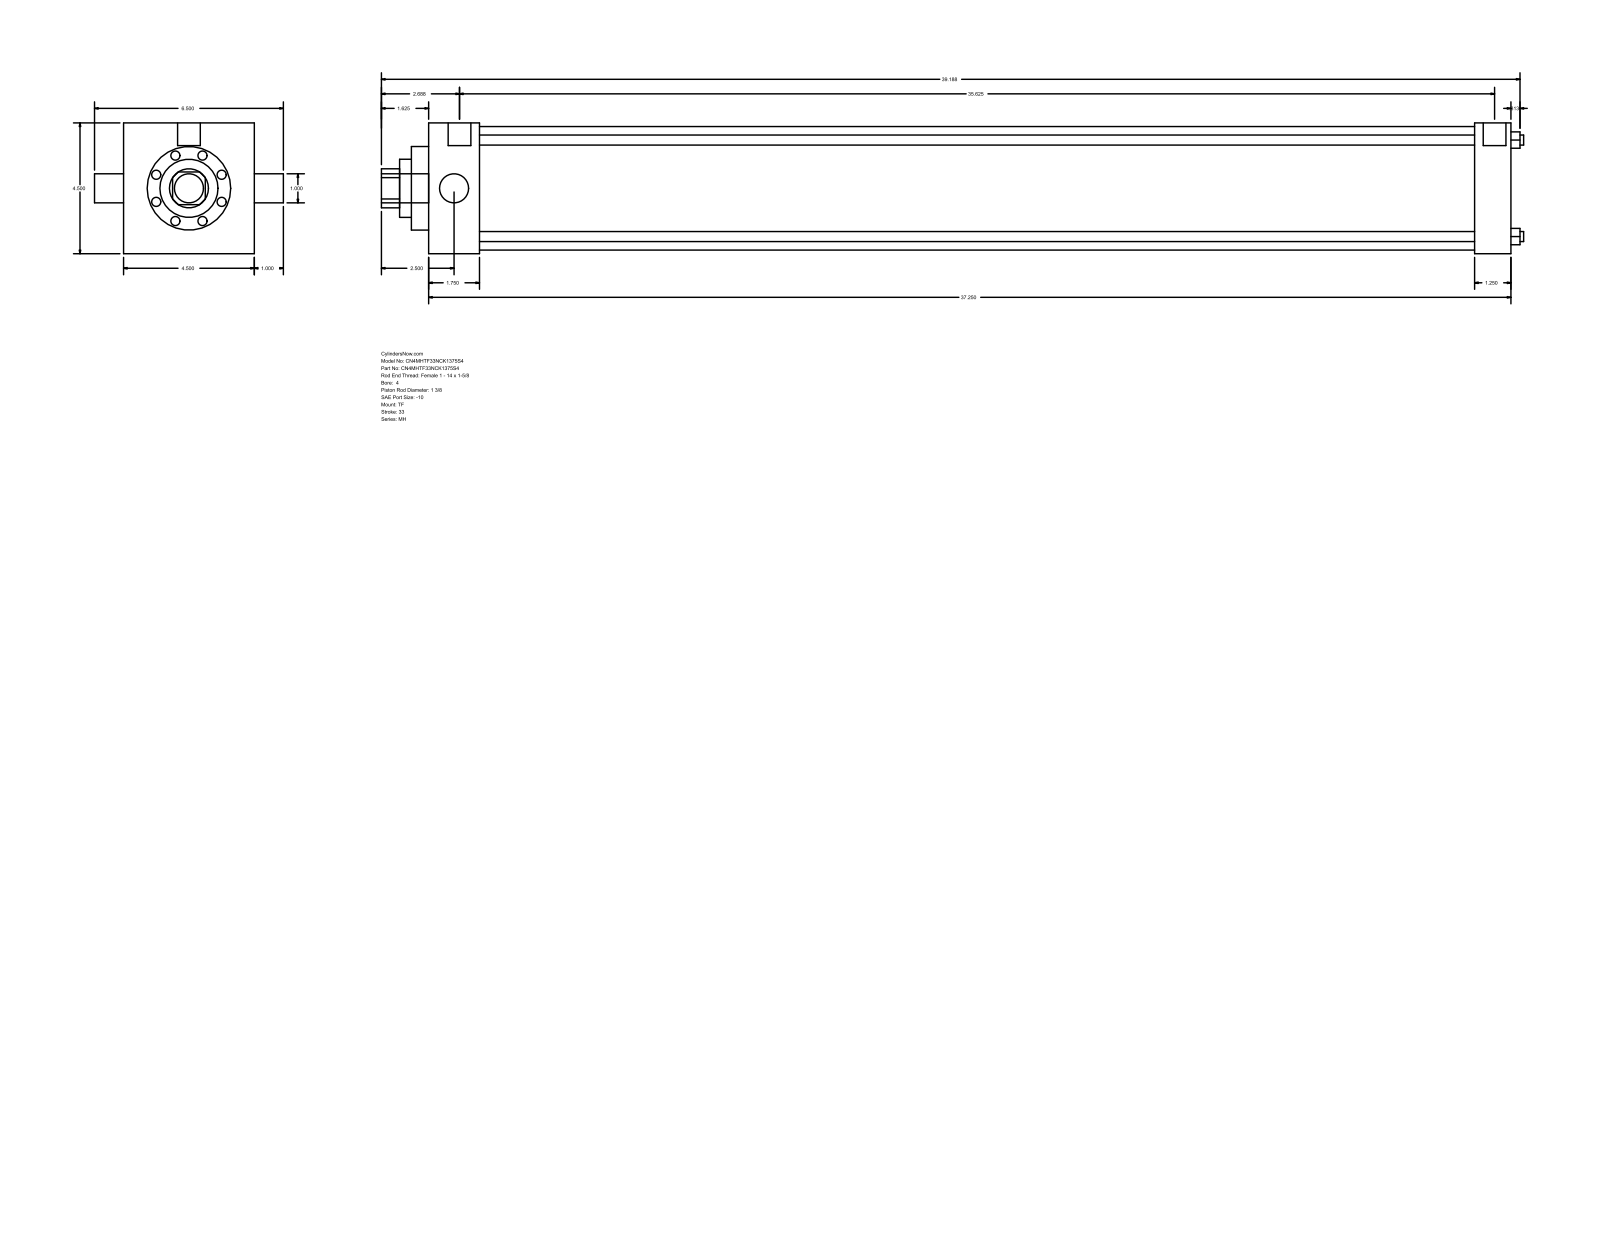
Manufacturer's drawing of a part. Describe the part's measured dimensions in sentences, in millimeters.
The part is named "MH_TF__0400_1.375". Its 3-D file was written by "GSSL Pune (CONFIG_CONTROL_DESIGN)". It is 0 solids with 86 faces: 61 planar, 25 cylindrical and 0 other. Overall it measures 998.54 by 165.1 by 114.3 millimeters. Round holes: 4 of diameter 8.76, 1 of diameter 25.4, 1 of diameter 34.92, 1 of diameter 50.8, 1 of diameter 73.03, 1 of diameter 107.95. Round bosses or shafts: 3 of diameter 8.73, 2 of diameter 19.84, 1 of diameter 25.4. Partial cylindrical surfaces (rounded edges, fillets, slot ends): 1 of radius 17.06. The main face-to-face distances are 114.3, 946.15, 44.45, 901.7, 914.4, 869.95, 31.75, 15.08, 59.53, 929.48. The hole center spacings are 59.62, 84.32, 119.25.
